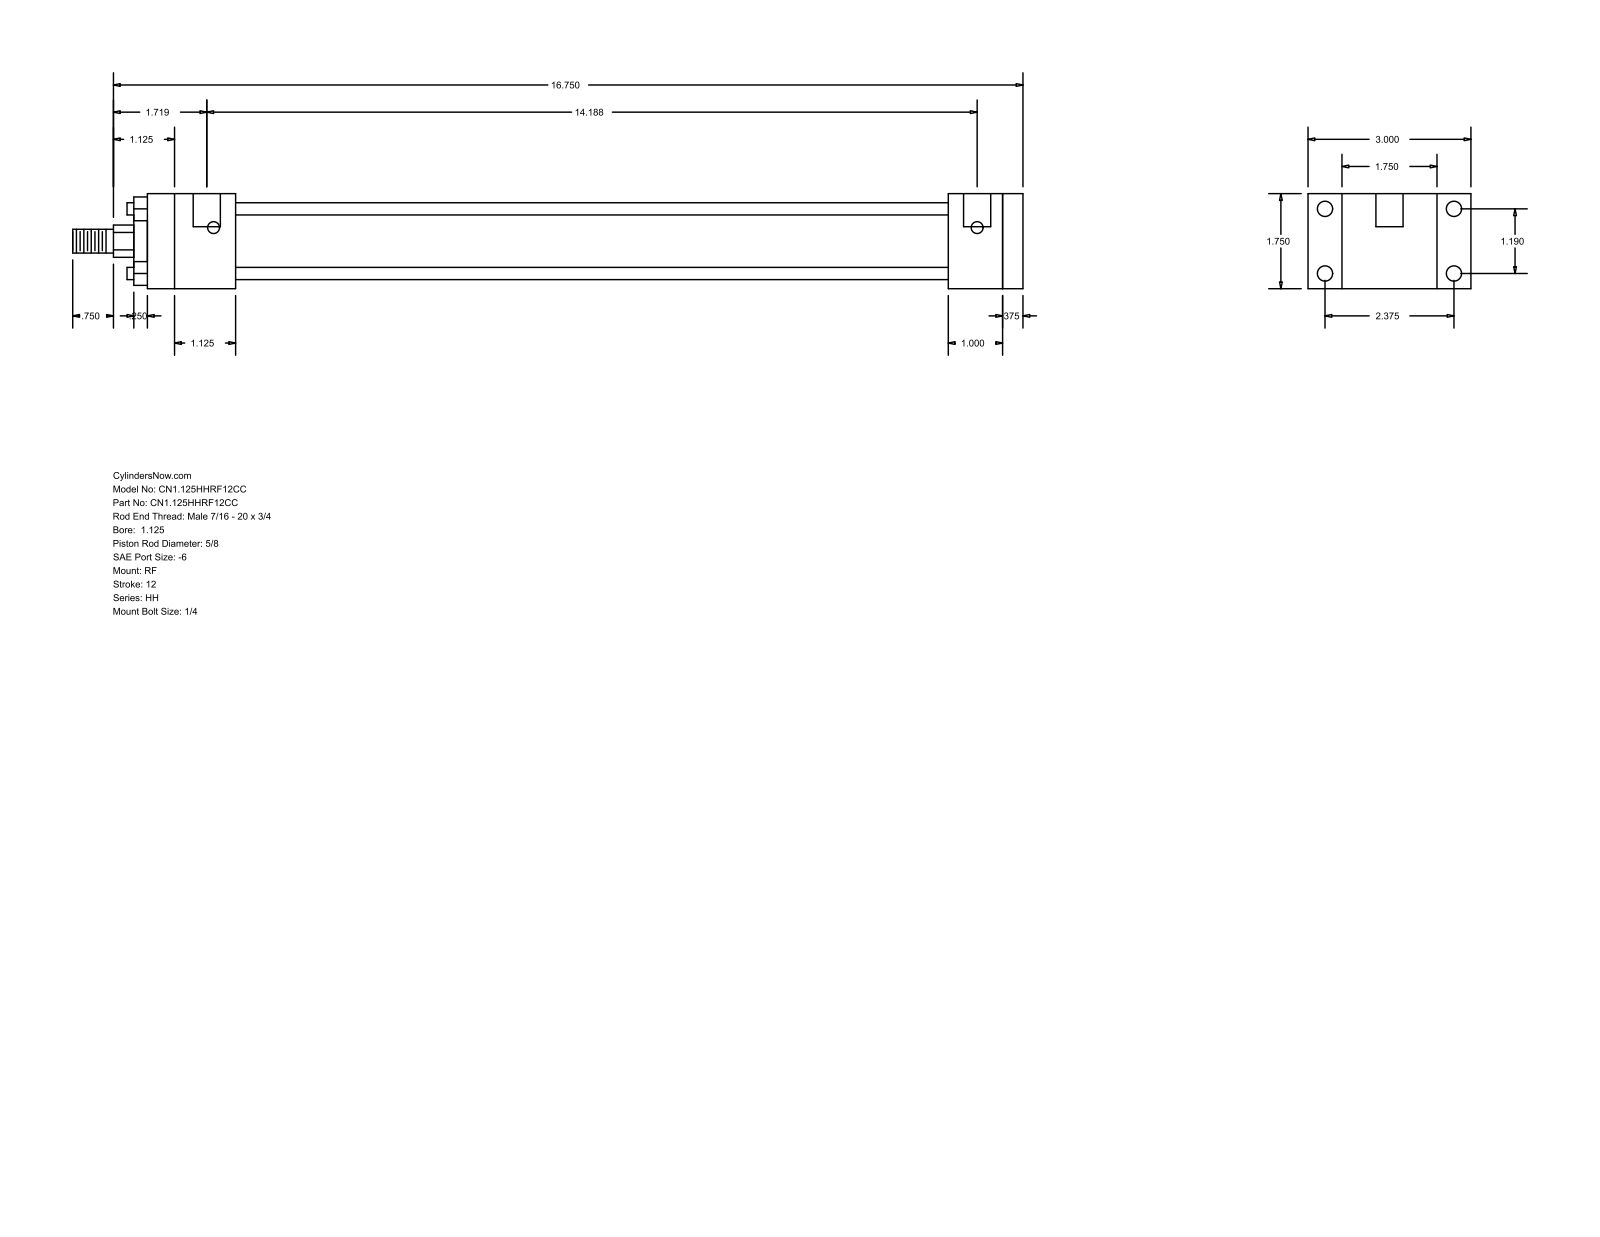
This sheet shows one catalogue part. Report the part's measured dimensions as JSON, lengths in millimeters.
{"part_name": "HH_RF__0112_0.625", "step_written_by": "GSSL Pune (CONFIG_CONTROL_DESIGN)", "units": "millimeters", "bodies": {"solids": 0, "faces": 92, "planar": 64, "cylindrical": 28, "other": 0}, "overall_size": [444.5, 76.2, 44.45], "round_holes": [[5.56, 4], [7.14, 4], [12.7, 2]], "round_bosses_or_shafts": [[5.71, 4], [34.92, 1], [28.57, 1], [15.88, 1], [11.11, 1]], "partial_cylinders_radius": [[7.54, 1]], "face_to_face_distances": [44.46, 9.52, 34.93, 409.57, 15.87, 358.78, 368.3, 333.37, 25.41, 41.27], "hole_center_spacings": [30.22, 60.32, 67.47, 357.19, 3.17, 360.36]}
